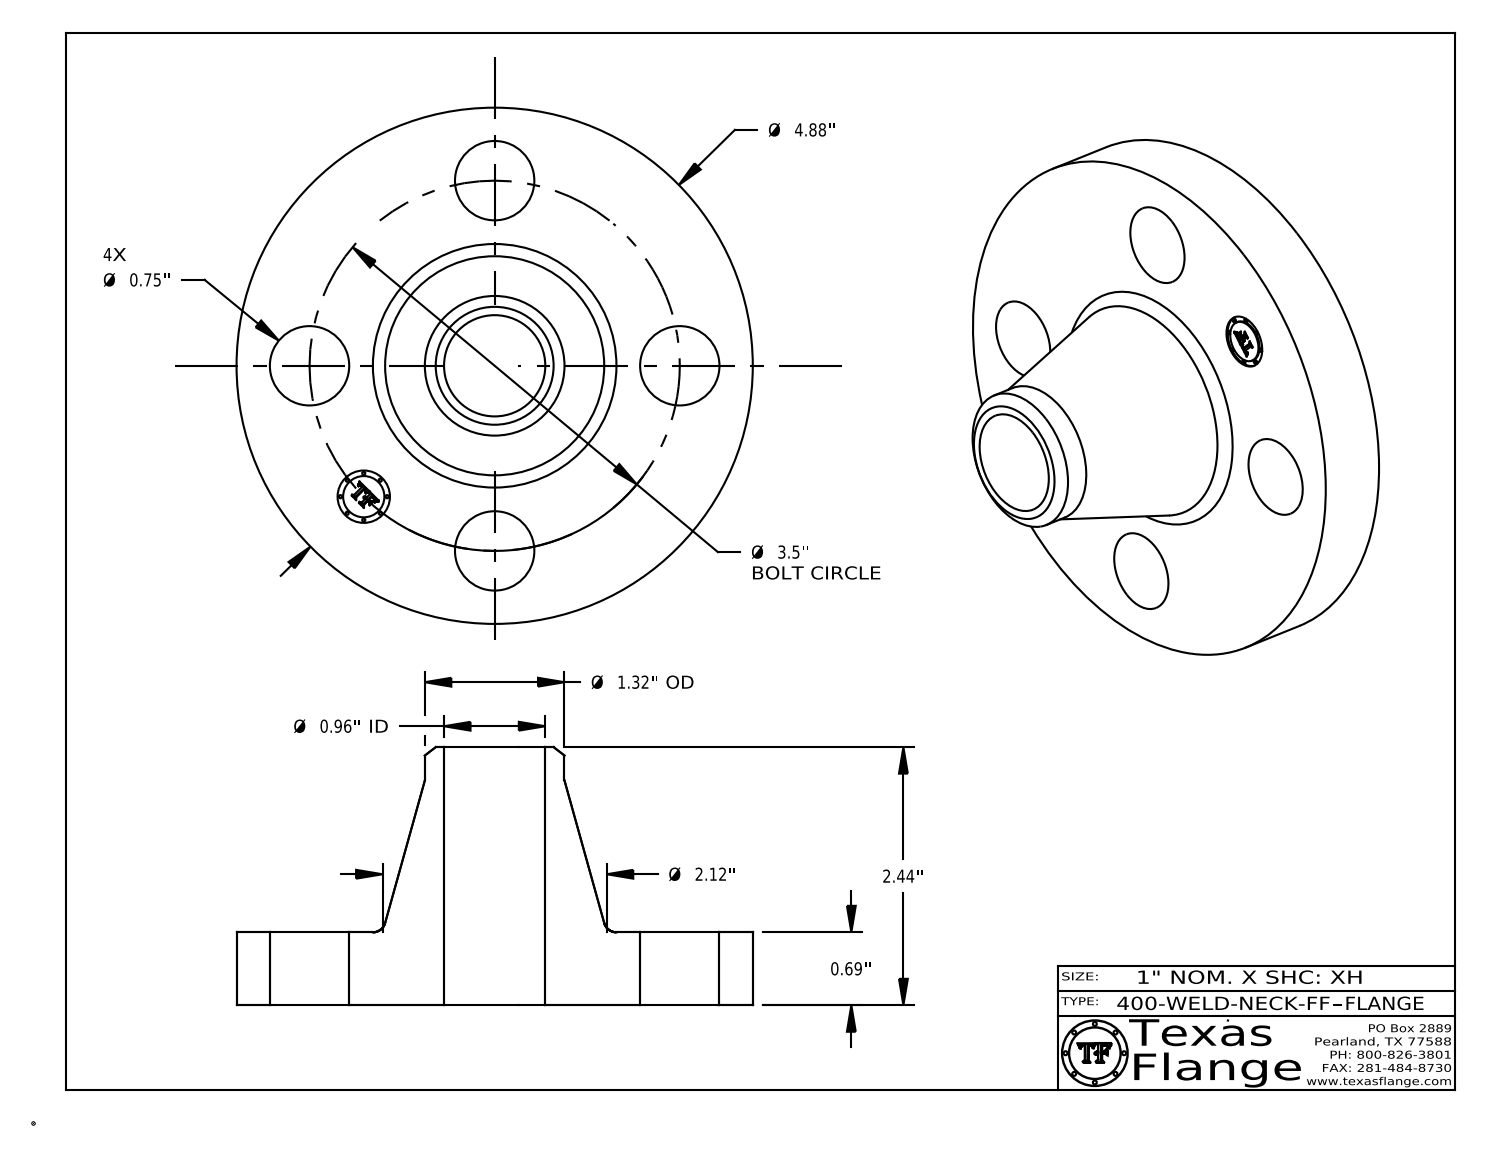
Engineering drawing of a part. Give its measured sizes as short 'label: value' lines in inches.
name: 400-WELD-NECK-FF
written by: CATIA V5 STEP AP214 (AUTOMOTIVE_DESIGN)
unit: in
bodies: 1 solid, 408 faces (368 planar, 34 cylindrical, 6 other)
size: 4.88 × 4.88 × 2.44
volume: 13.75 in³; area: 63.74 in²
holes: 4× ⌀0.75, 1× ⌀0.495, 1× ⌀0.957
bosses: 8× ⌀0.03, 1× ⌀4.88, 1× ⌀1.32, 1× ⌀0.39
face distances: 0.69, 2.44, 1.75, 0.015, 0.675, 1.765, 0.148, 0.145, 0.027, 0.096
hole spacings: 1.75, 2.475, 1.339, 3.233, 3.5
